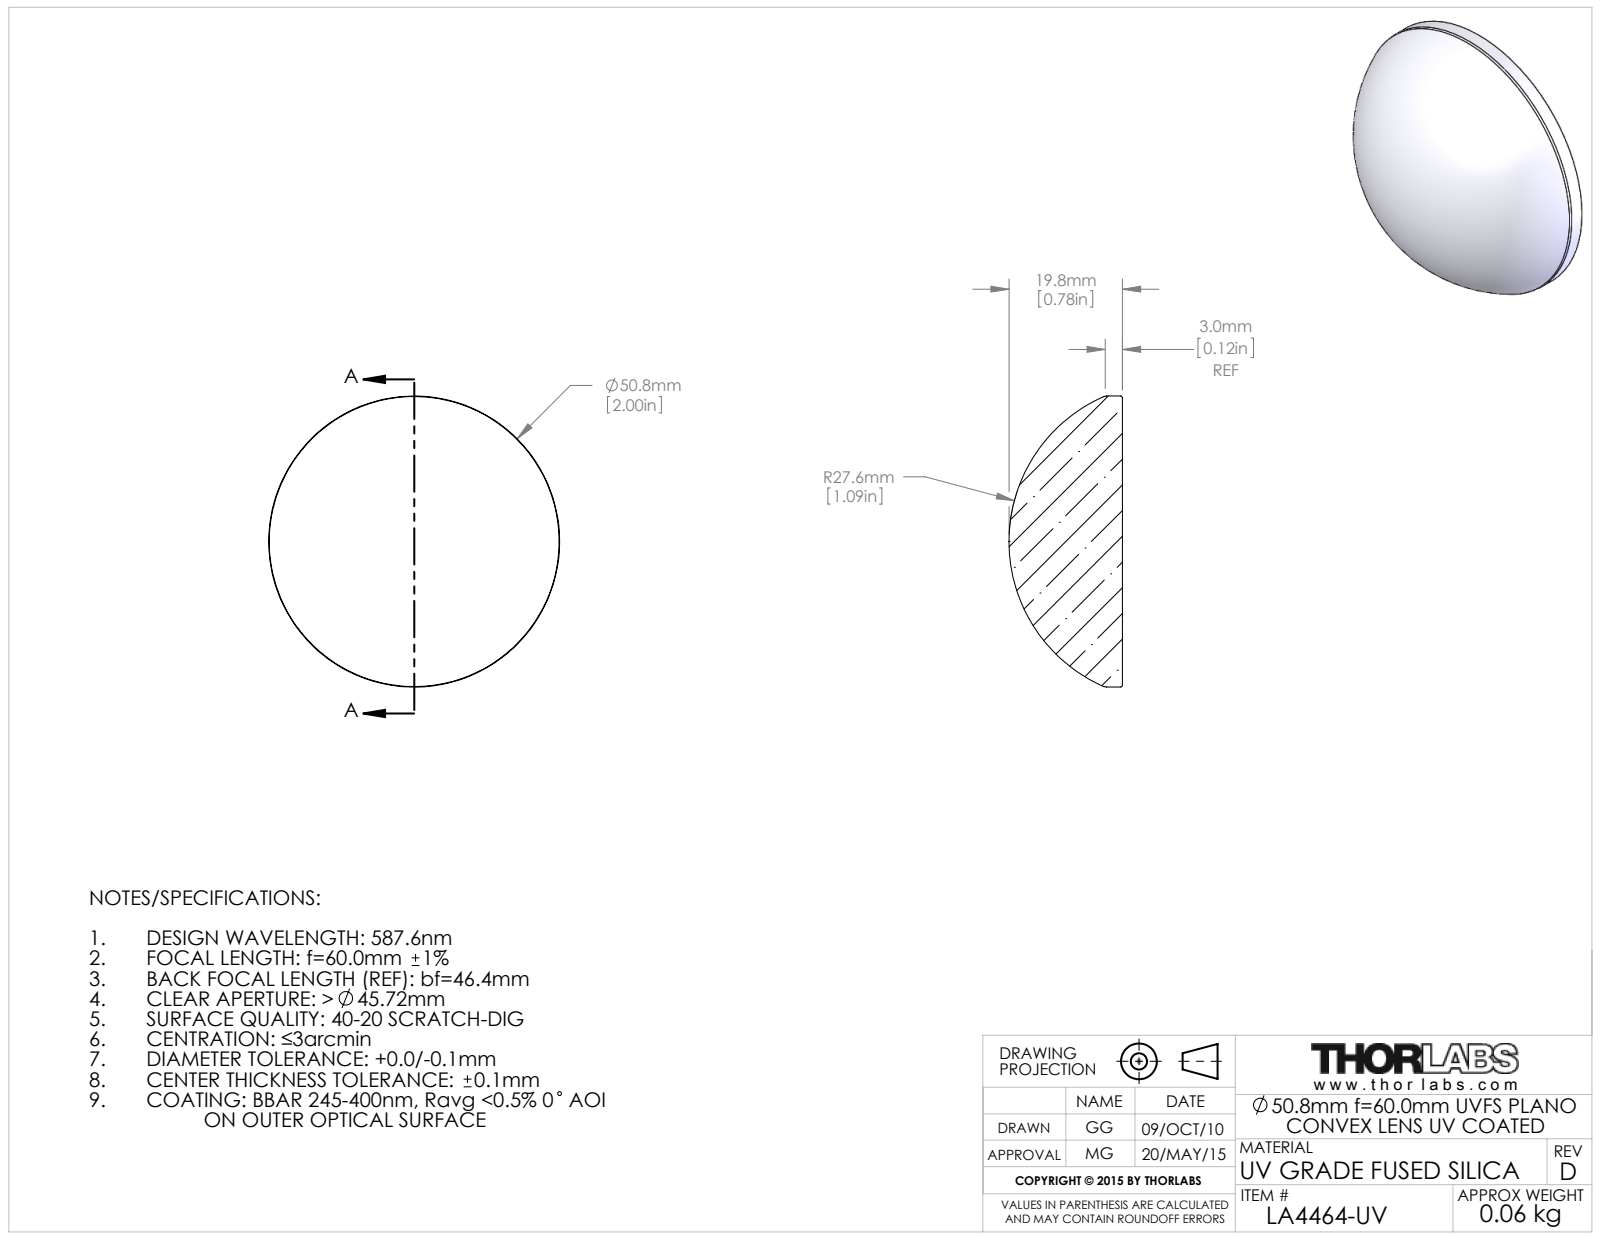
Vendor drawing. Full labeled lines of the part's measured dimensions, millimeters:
Part name (STEP PRODUCT): 4292-E0W
STEP written by: SolidWorks 2014 (CONFIG_CONTROL_DESIGN)
Units: millimetres
Bodies: 1 solid, 9 faces (1 planar, 2 cylindrical, 6 other)
Overall size (bounding box): 50.8 × 50.8 × 19.8
Volume: 25 582 mm³ · Surface area: 5 394 mm²
Round bosses / shafts (diameter × count): ⌀50.8 ×1
